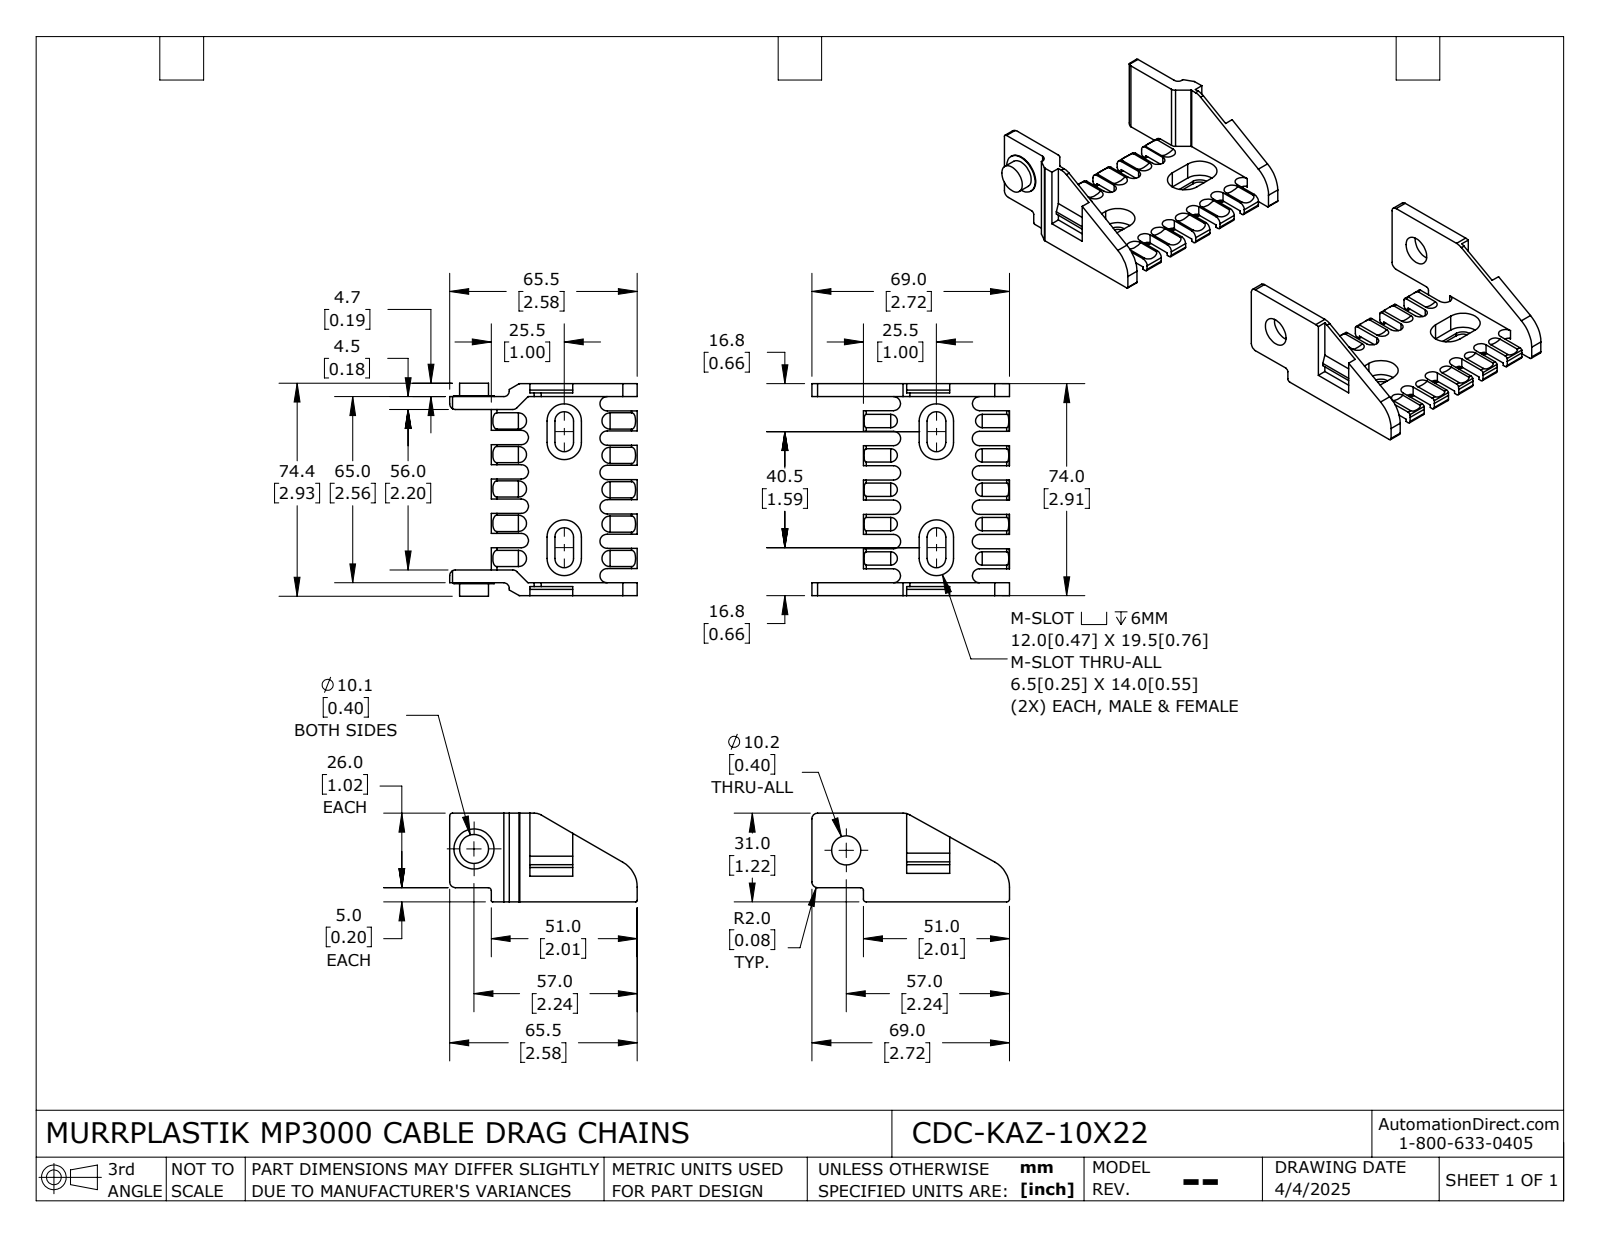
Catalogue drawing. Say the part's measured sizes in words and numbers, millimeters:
The part is named "CDC-KAZ-10X22". Its 3-D file was written by "SolidWorks 2024 (AUTOMOTIVE_DESIGN)". It is 2 solids with 441 faces: 234 planar, 187 cylindrical and 20 other. Overall it measures 195.5 by 74.4 by 31 millimeters. Its volume is 51 530 cubic millimeters and its surface area 30 926 square millimeters. Round holes: 1 of diameter 10.2. Round bosses or shafts: 1 of diameter 14, 1 of diameter 10.1. Partial cylindrical surfaces (rounded edges, fillets, slot ends): 18 of radius 2.5, 15 of radius 1, 13 of radius 2, 13 of radius 7, 8 of radius 3.25, 8 of radius 6, 4 of radius 0.5, 4 of radius 2.45. The main face-to-face distances are 4.5, 69.5, 65, 7, 3.5, 74, 9, 60.5, 24, 3.2.
